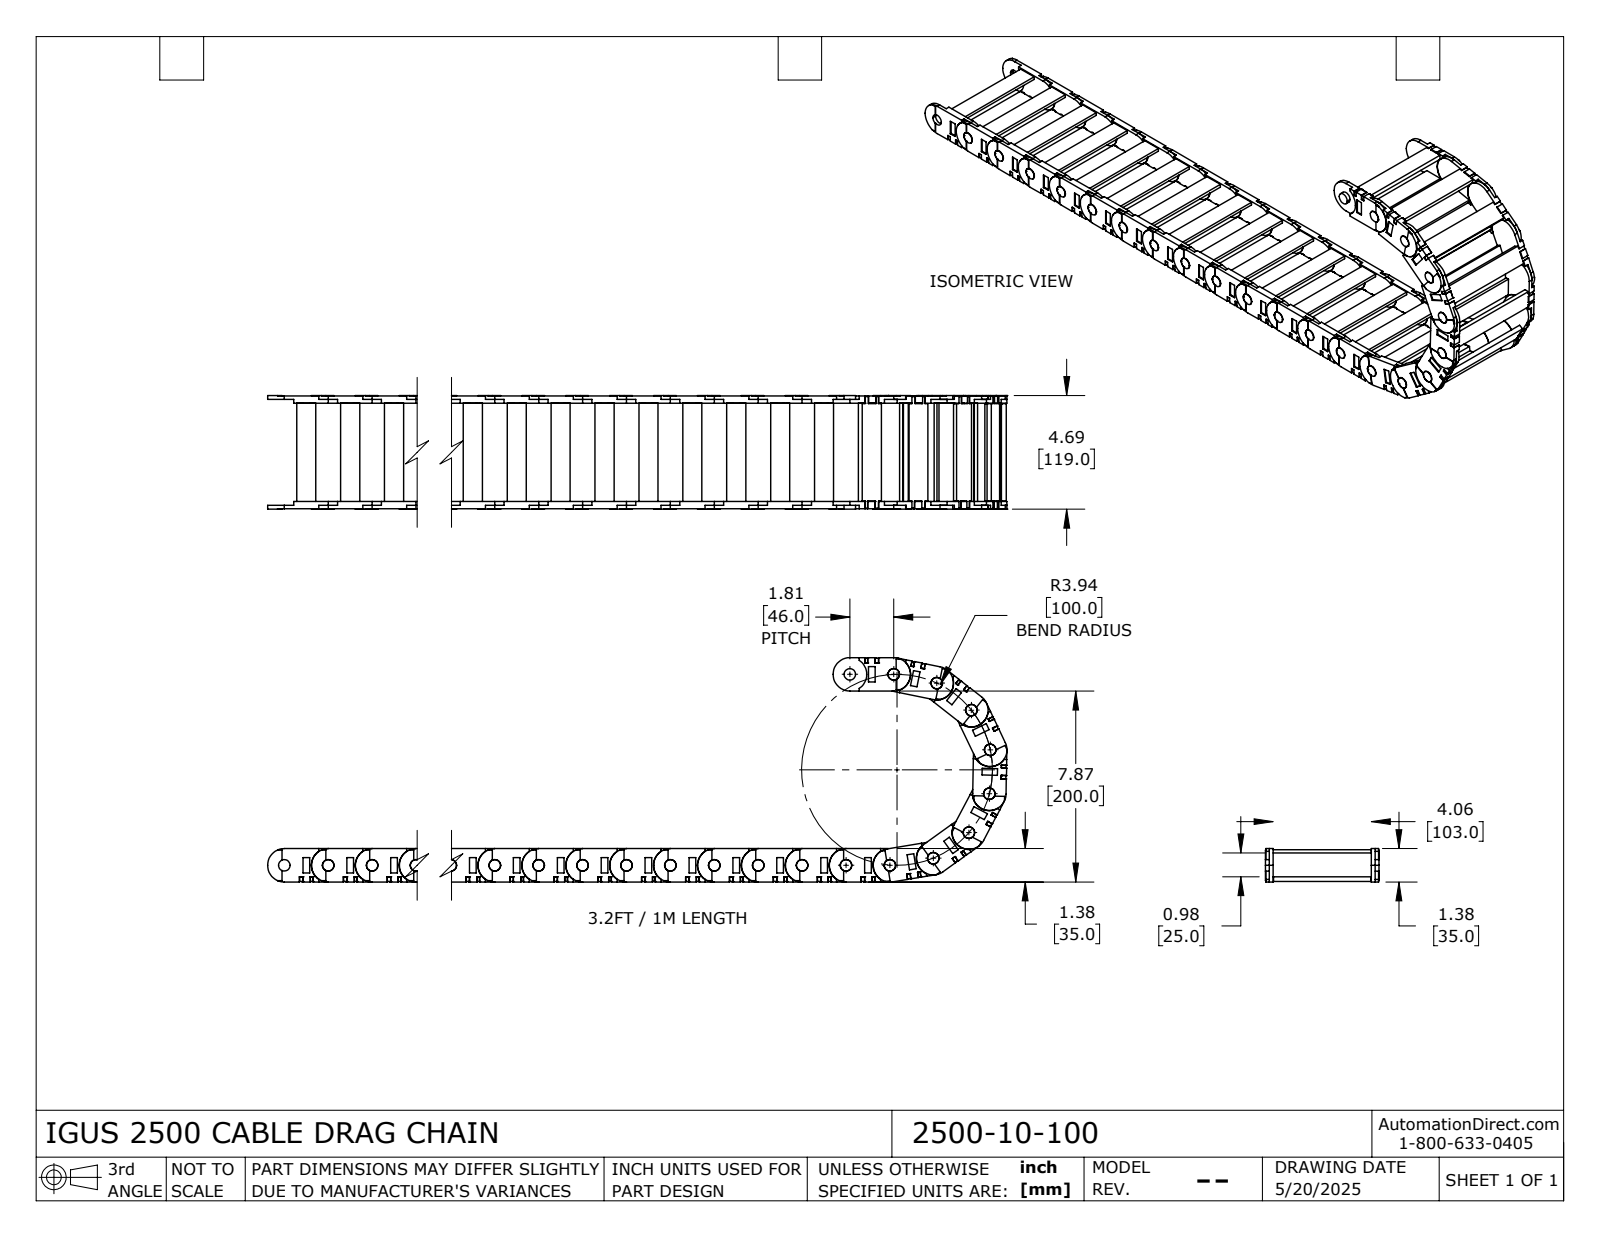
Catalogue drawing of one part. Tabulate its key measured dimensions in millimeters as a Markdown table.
| quantity | value |
| --- | --- |
| part name | 2500_10_100 |
| STEP written by | SolidWorks 2024 (AUTOMOTIVE_DESIGN) |
| units | millimeters |
| bodies | 66 solids, 2398 faces (1870 planar, 528 cylindrical, 0 other) |
| overall size | 784.1 × 235 × 119 |
| volume | 910 300 mm³ |
| surface area | 526 300 mm² |
| round holes (diameter × count) | 12 × 22 |
| round bosses / shafts (diameter × count) | 12 × 22, 35 × 21 |
| partial cylindrical surfaces (radius × count) | 17.7 × 23, 17.5 × 2 |
| main face-to-face distances | 4, 107, 111, 3.6, 3.4, 7.6, 110.6, 114.6, 5, 25 |
| hole center spacings | 46, 92, 138, 184, 230, 276, 322, 368 |
